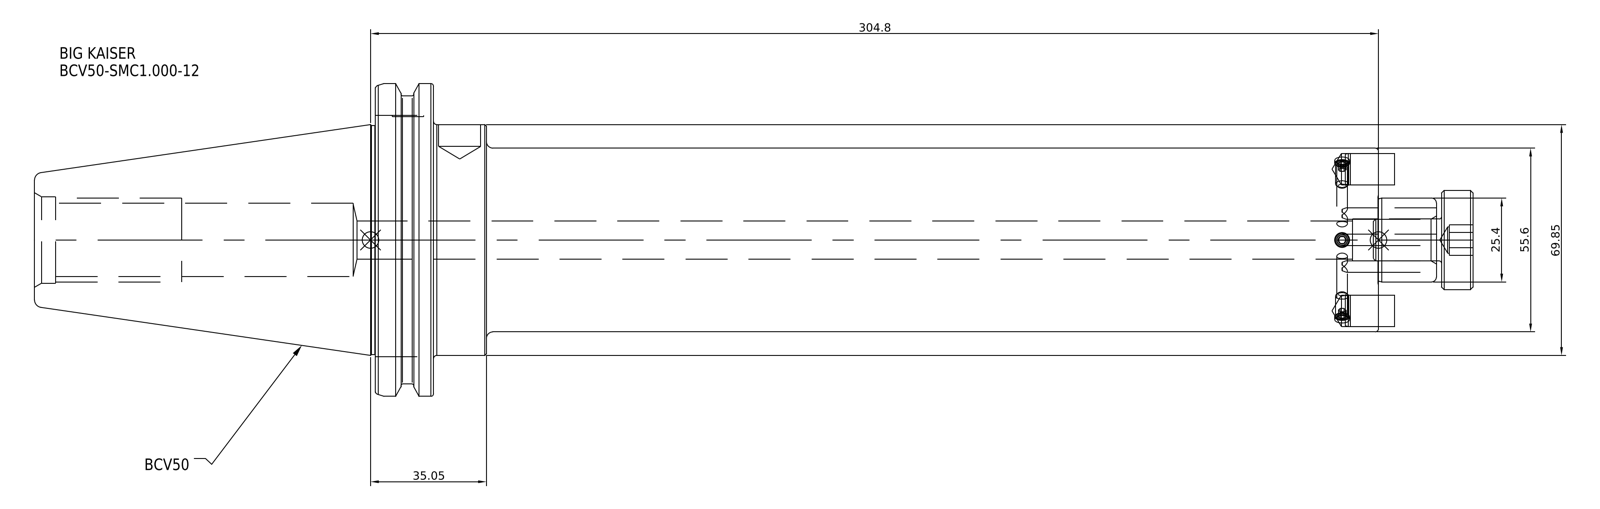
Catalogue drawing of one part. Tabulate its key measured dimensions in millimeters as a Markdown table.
| quantity | value |
| --- | --- |
| part name | BCV50-SMC1_000-12 |
| STEP written by | SolidWorks 2021 (CONFIG_CONTROL_DESIGN) |
| units | millimeters |
| bodies | 1 solid, 38 faces (18 planar, 14 cylindrical, 6 other) |
| overall size | 411.3 × 98.43 × 98.43 |
| volume | 1 070 000 mm³ |
| surface area | 98 229 mm² |
| round holes (diameter × count) | 11.51 × 1 |
| round bosses / shafts (diameter × count) | 98.43 × 1, 91.29 × 1, 69.85 × 1, 55.6 × 1 |
| main face-to-face distances | 17.55, 285.75, 303.3, 269.75, 16, 33.55, 406.4, 136.65, 120.65, 103.1 |
